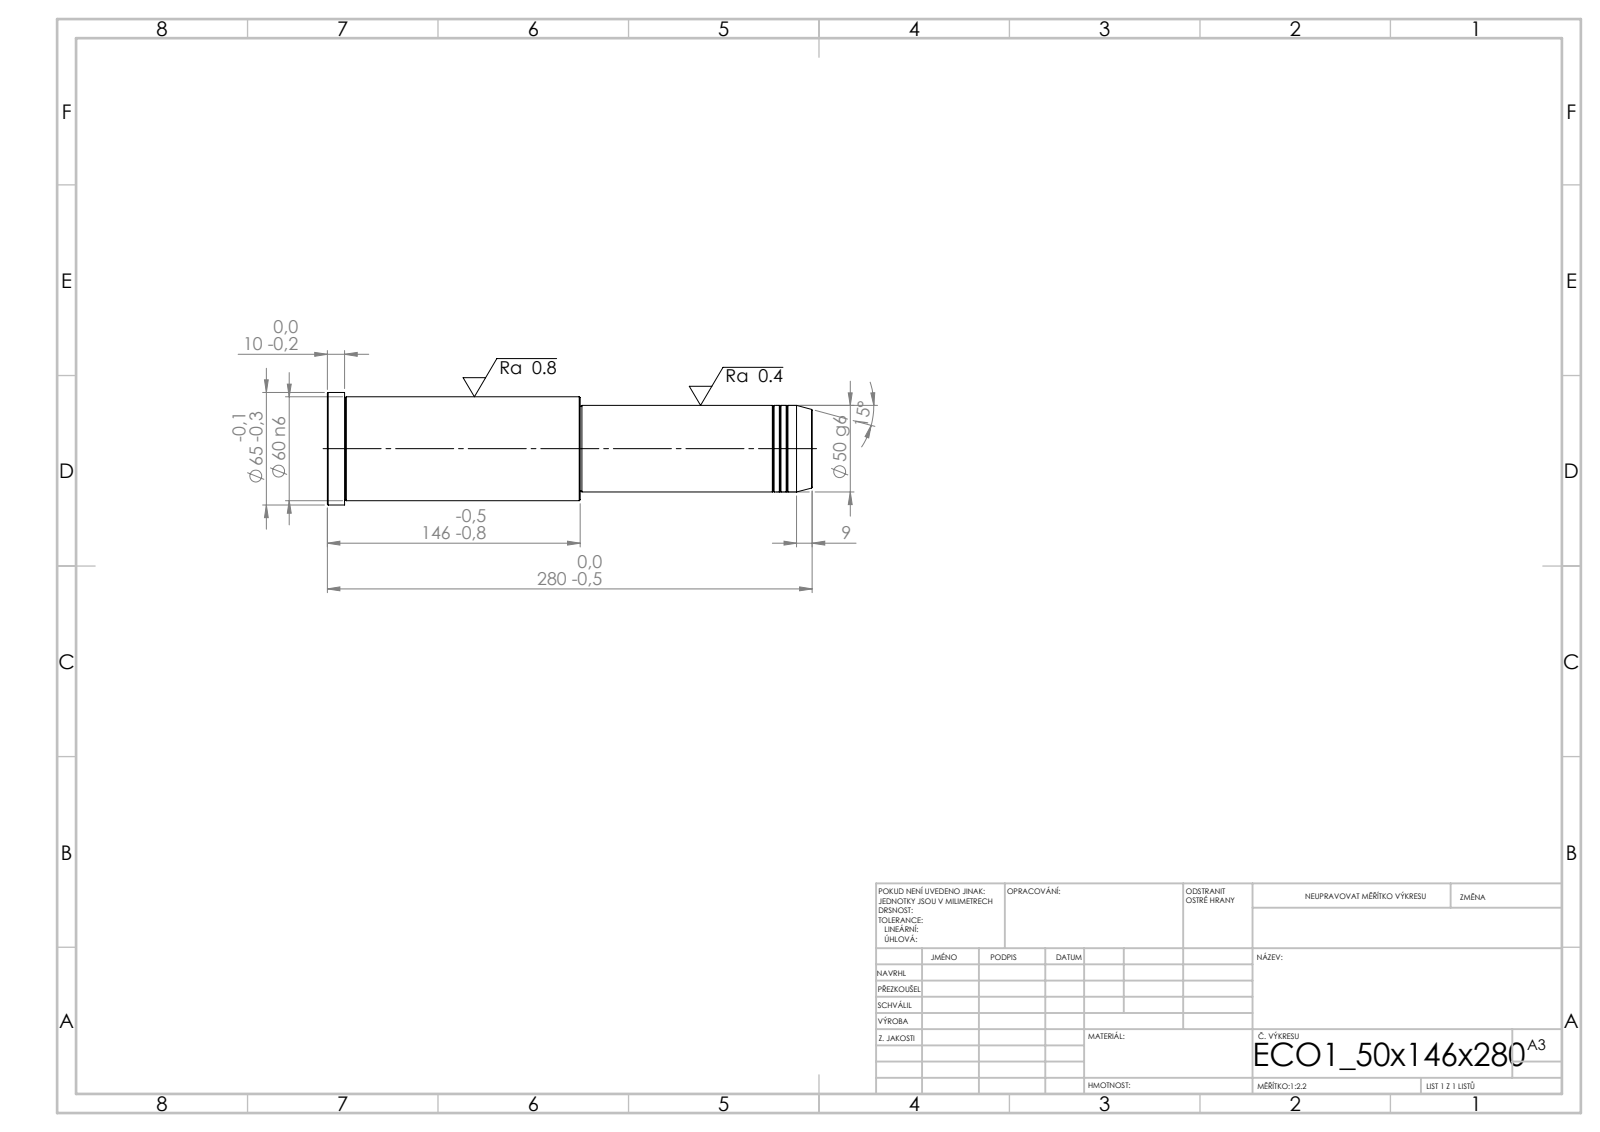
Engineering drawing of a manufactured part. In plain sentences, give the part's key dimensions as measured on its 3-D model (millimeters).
Its 3-D file was written by "SolidWorks 2019 (CONFIG_CONTROL_DESIGN)". It is 1 solid with 43 faces: 5 planar, 14 cylindrical and 24 other. Overall it measures 280 by 65 by 65 millimeters. Its volume is 678 785 cubic millimeters and its surface area 55 366 square millimeters. Round bosses or shafts: 1 of diameter 65, 1 of diameter 60, 1 of diameter 50, 1 of diameter 49. The main face-to-face distances are 280, 134, 146, 270, 136, 10, 133, 1, 137, 147.
